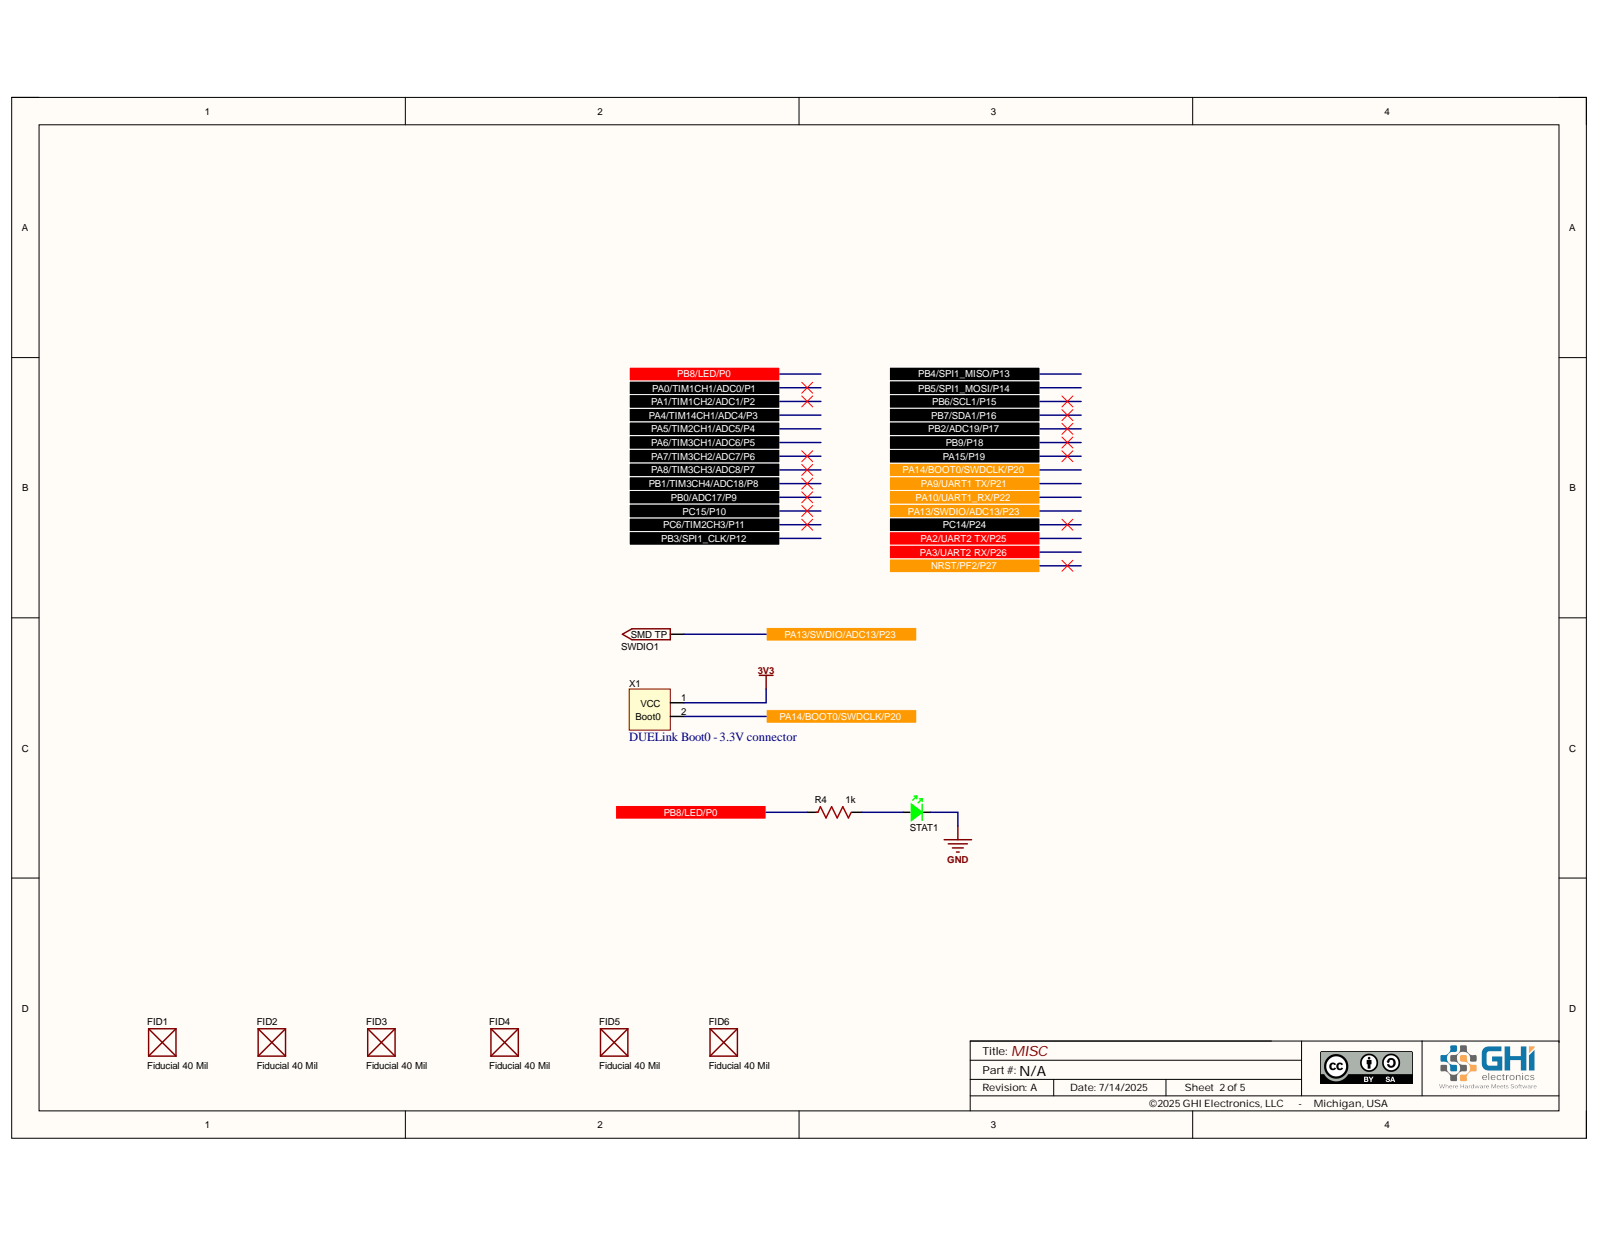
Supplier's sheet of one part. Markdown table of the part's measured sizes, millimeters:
| quantity | value |
| --- | --- |
| part name | PCB; Board; STAT1; 0603 LED Green (+5 more) |
| STEP written by | Open CASCADE 7.5 (AUTOMOTIVE_DESIGN) |
| units | millimeters |
| bodies | 173 solids, 3480 faces (2277 planar, 817 cylindrical, 386 other) |
| overall size | 60 × 57 × 17.36 |
| volume | 2 971 mm³ |
| surface area | 9 427 mm² |
| round holes (diameter × count) | 1.02 × 8, 2.5 × 4, 3 × 4, 1.02 × 2, 0.36 × 1 |
| round bosses / shafts (diameter × count) | 0.51 × 2 |
| partial cylindrical surfaces (radius × count) | 0.12 × 35, 0.15 × 14, 0.12 × 12, 3.5 × 4, 0.17 × 2, 0.18 × 2, 0.18 × 2, 0.25 × 2 |
| main face-to-face distances | 1, 7.65, 7.45, 6.45, 6.65, 0.64, 1.1, 7.75, 7.55, 0.99 |
| hole center spacings | 2.54, 5.08, 7.62, 10.16, 12.7, 8.61, 11.15, 13.69 |
